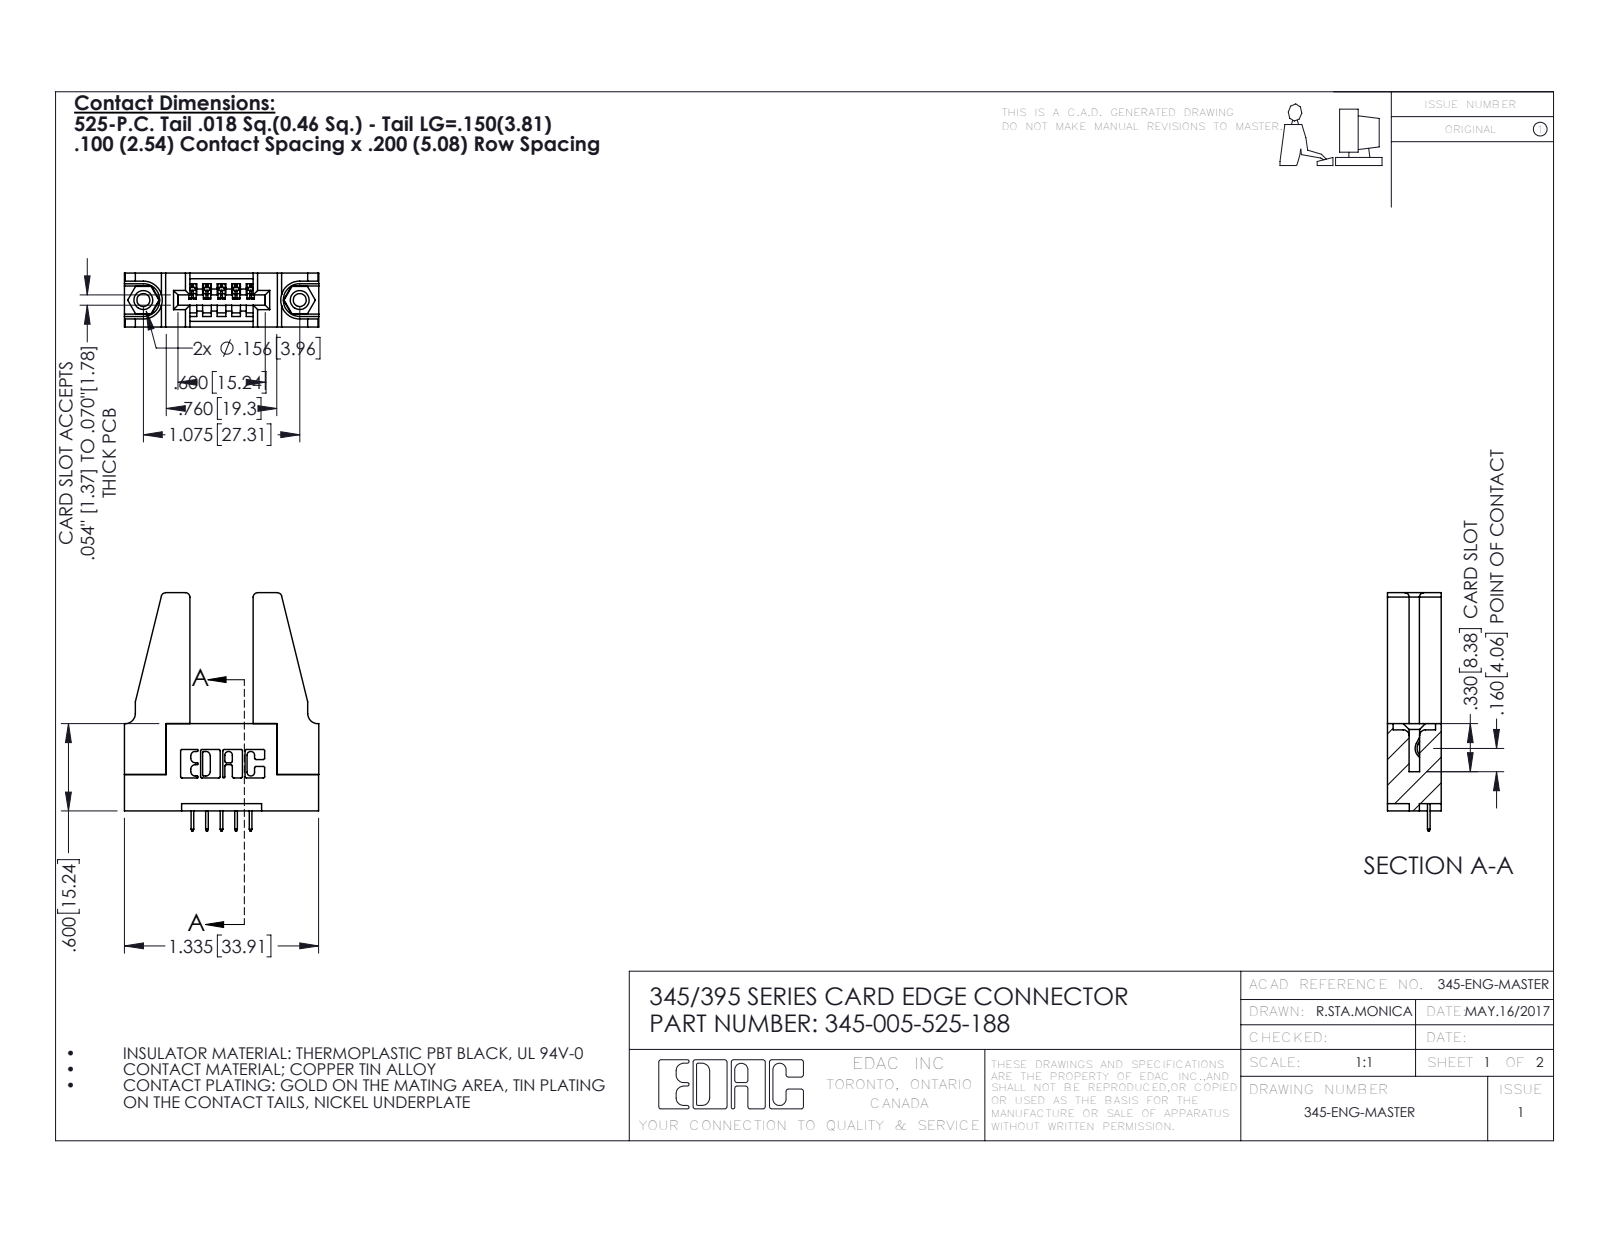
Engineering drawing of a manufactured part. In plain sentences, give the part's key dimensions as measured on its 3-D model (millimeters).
The part is named "345-292-001_345-293-125; 345-250-001_345-250-001-102; 345-220-078_345-220-088; 345 Part_Flush Mounting Lugs - 0.156 Dia-TH (+1 more)". Its 3-D file was written by "SolidWorks 2020 (CONFIG_CONTROL_DESIGN)". It is 10 solids with 560 faces: 382 planar, 162 cylindrical and 16 other. Overall it measures 41.6 by 33.9 by 9.4 millimeters. Its volume is 6 150 cubic millimeters and its surface area 6 412 square millimeters. Round holes: 2 of diameter 2.3, 2 of diameter 3.2, 2 of diameter 4, 1 of diameter 1.6. Round bosses or shafts: 2 of diameter 3.9. Partial cylindrical surfaces (rounded edges, fillets, slot ends): 22 of radius 0.3, 10 of radius 0.2, 8 of radius 0.8, 6 of radius 0.2, 6 of radius 0.8, 3 of radius 0.7, 2 of radius 0.8, 2 of radius 1. The main face-to-face distances are 9.4, 5.1, 1.8, 7.6, 15.2, 6.4, 3.8, 3.8, 8.9, 2. The hole center spacings are 6.9, 21.5, 27.3.
